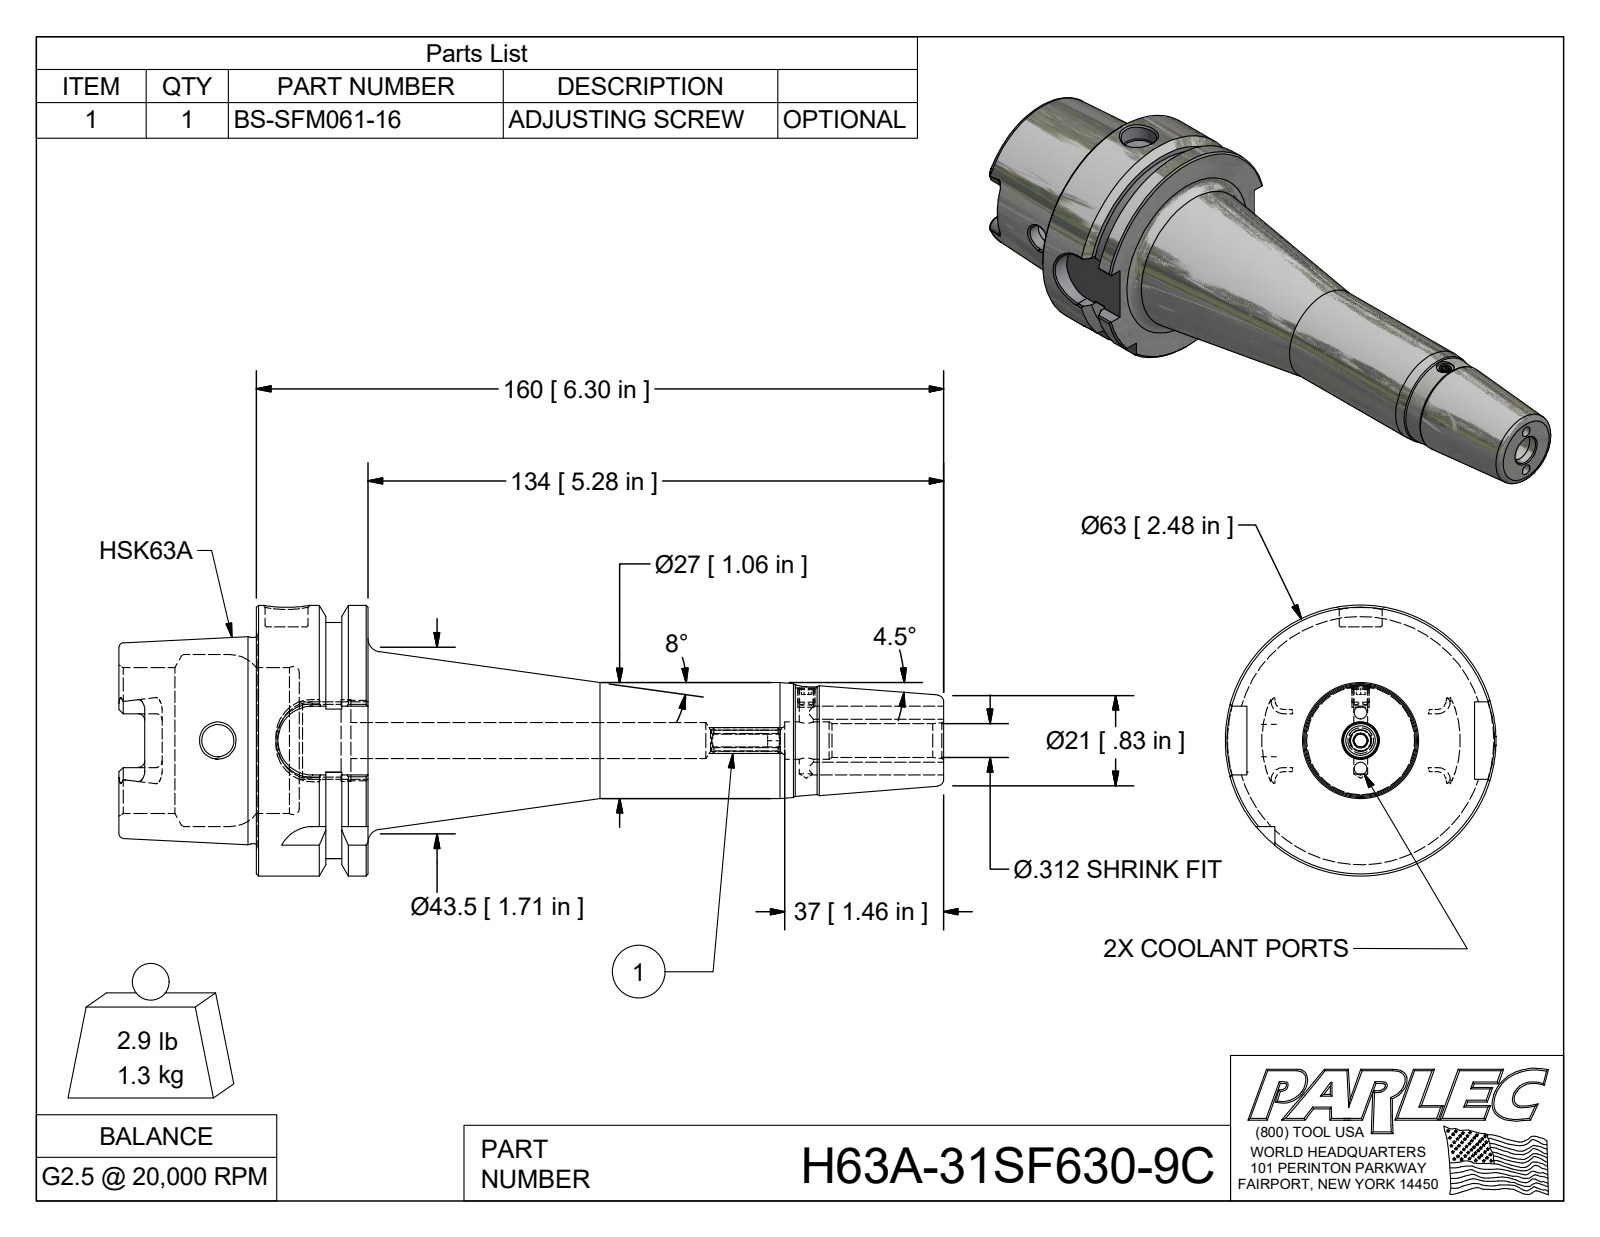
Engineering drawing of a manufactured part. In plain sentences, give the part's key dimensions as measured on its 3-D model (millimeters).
The part is named "H63A-31SF630-9C". Its 3-D file was written by "Autodesk Inventor 2018 (AUTOMOTIVE_DESIGN)". It is 1 solid with 153 faces: 53 planar, 42 cylindrical and 58 other. Overall it measures 192 by 63 by 63 millimeters. Its volume is 166 835 cubic millimeters and its surface area 37 654 square millimeters. Round holes: 2 of diameter 3, 1 of diameter 3.25, 1 of diameter 4.92, 1 of diameter 5, 1 of diameter 7.5, 1 of diameter 7.92, 1 of diameter 8.4, 1 of diameter 8.68, 1 of diameter 10, 1 of diameter 16.92, 1 of diameter 19.02, 1 of diameter 34. Round bosses or shafts: 1 of diameter 63, 1 of diameter 48.04, 1 of diameter 27. Partial cylindrical surfaces (rounded edges, fillets, slot ends): 6 of radius 1.5, 4 of radius 2.88, 4 of radius 8, 1 of radius 27.5. The main face-to-face distances are 26, 6.12, 9.88, 10, 16, 32, 42, 58, 51.88, 19.88. The hole center spacings are 6.5, 13, 121.02.
